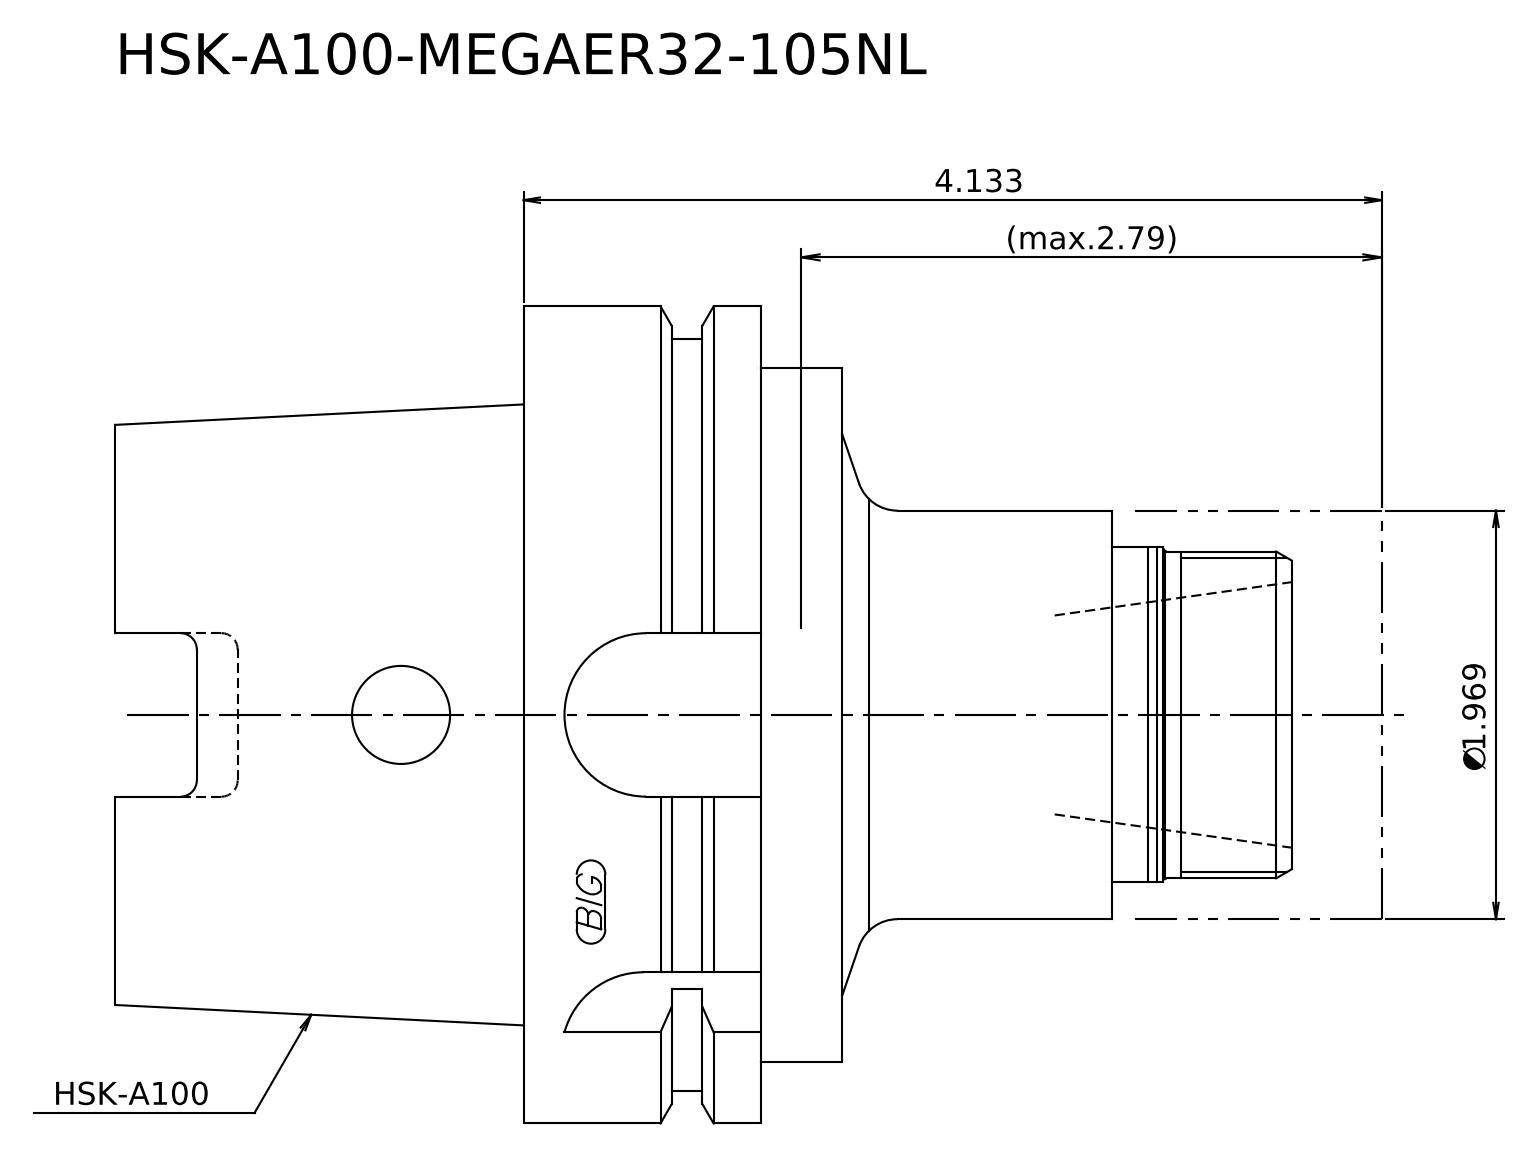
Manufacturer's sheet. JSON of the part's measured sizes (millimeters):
{"step_written_by": "Kubotek KeyCreator 2011 V10.0.2 (22737) (automotive_design)", "units": "millimeters", "bodies": {"solids": 2, "faces": 24, "planar": 10, "cylindrical": 8, "other": 6}, "overall_size": [155, 100, 100], "volume_mm3": 648793, "surface_area_mm2": 55996, "round_bosses_or_shafts": [[100, 1], [92, 1], [85, 1], [50, 1], [41, 1], [40, 1]], "face_to_face_distances": [50, 29, 79, 10, 39, 89, 35.8, 45.8, 74.8, 124.8]}
